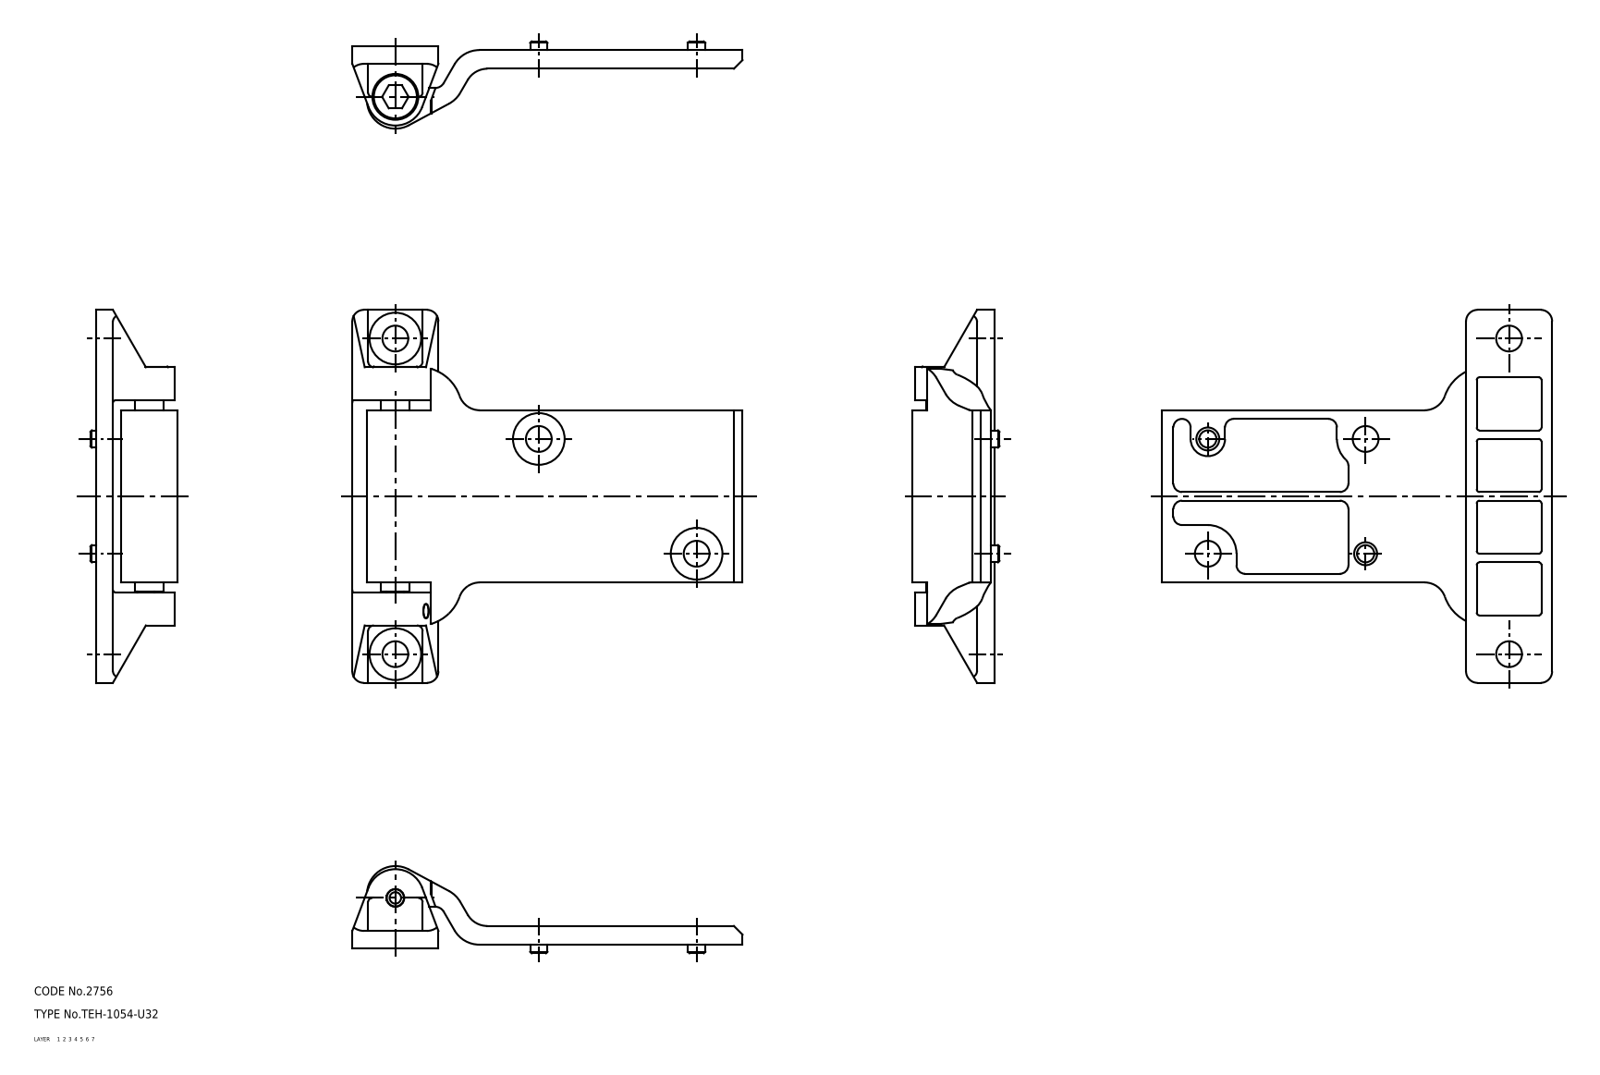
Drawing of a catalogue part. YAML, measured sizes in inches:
part_name: "shaft_mr; screw_mr; hinge pieces_B_mr; hinge pieces_A_mr (+1 more)"
step_written_by: "CADfix (AUTOMOTIVE_DESIGN)"
units: inches
bodies: {solids: 4, faces: 196, planar: 0, cylindrical: 0, other: 196}
overall_size: [5.354, 5.118, 1.197]
volume: 5.368
surface_area: 63.83
